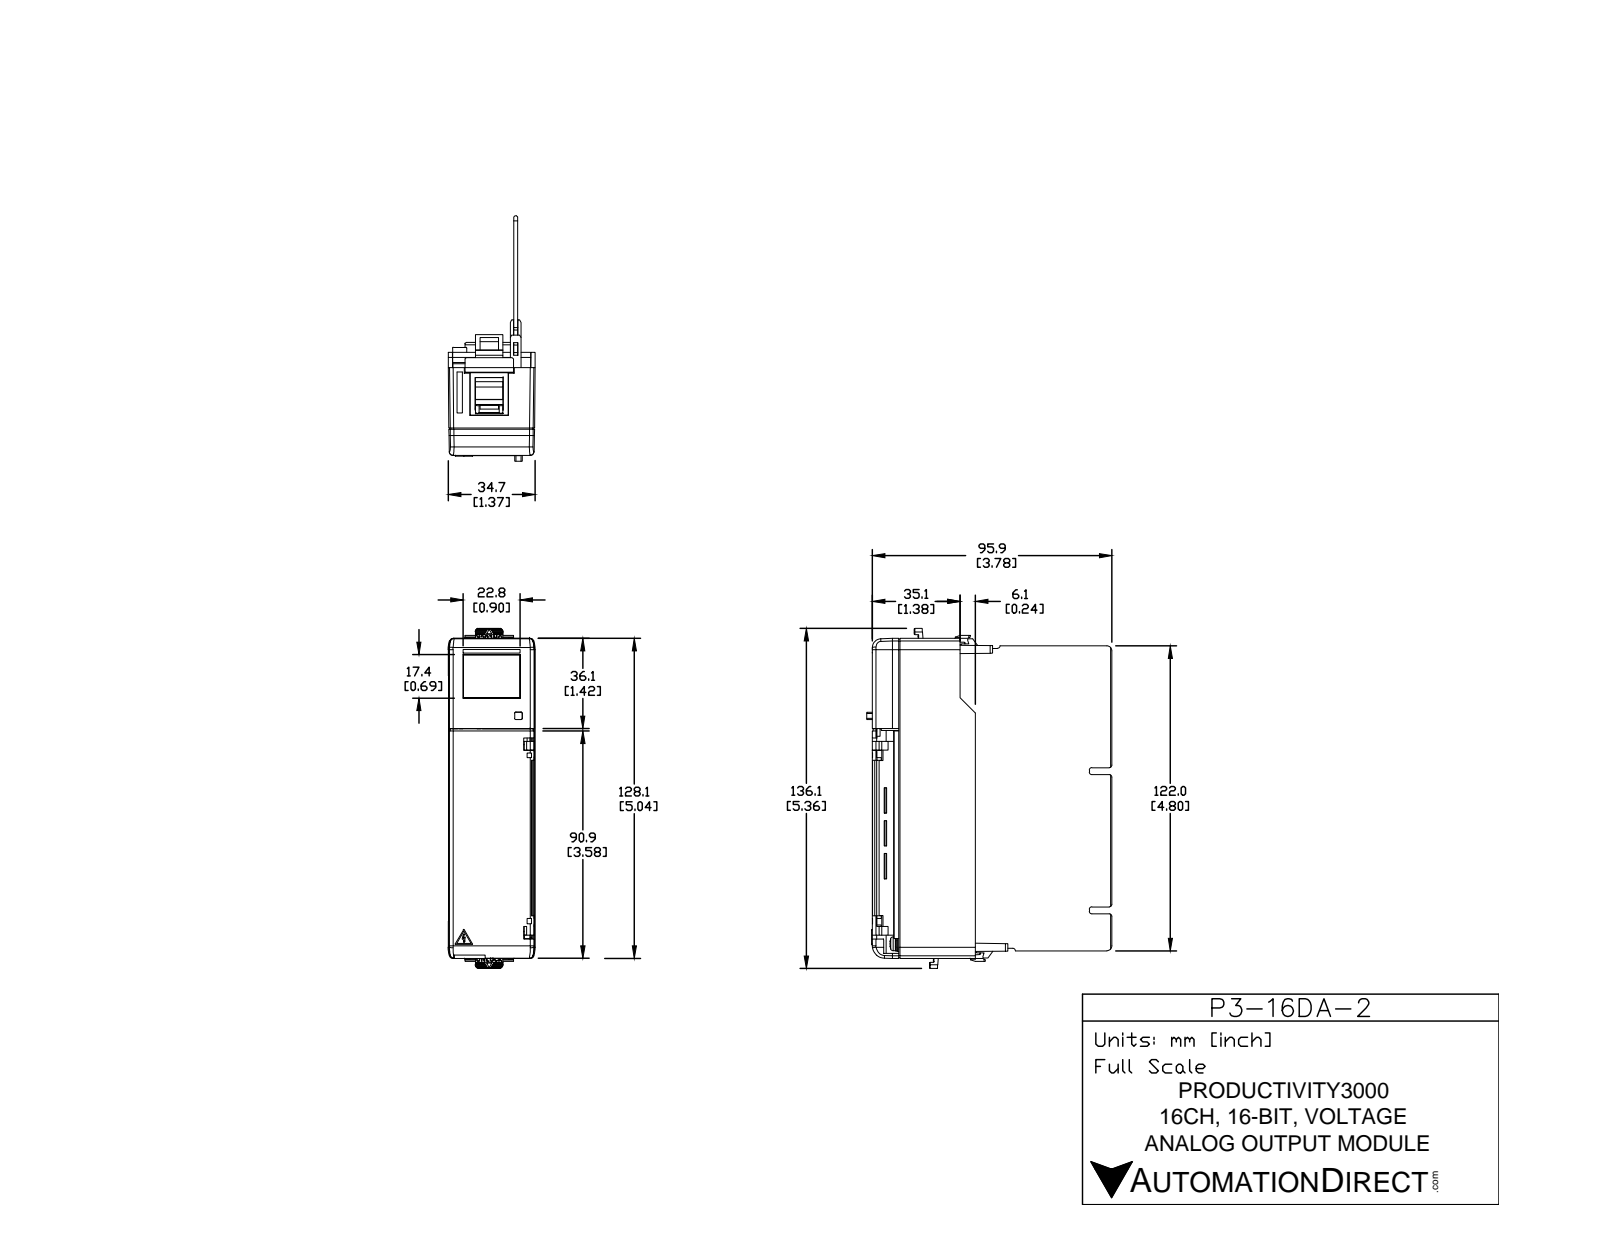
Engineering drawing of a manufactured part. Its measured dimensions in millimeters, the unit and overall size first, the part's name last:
Units: millimetres
Overall size (bounding box): 136.08 × 98.18 × 34.8
Round holes (diameter × count): ⌀3.2 ×22, ⌀5 ×2, ⌀1.8 ×1
Round bosses / shafts (diameter × count): ⌀5.5 ×22, ⌀3 ×22, ⌀2.4 ×20, ⌀5.6 ×2, ⌀2.2 ×2, ⌀2 ×2, ⌀1.5 ×1
Partial cylindrical surfaces — rounded edges, fillets, slot ends (radius × count): R0.5 ×95, R1 ×33, R0.3 ×29, R1.67 ×22, R1.5 ×13, R2 ×6, R0.2 ×5, R0.1 ×4
Main face-to-face distances: 1.6, 1.7, 28.23, 26.53, 32.56, 22.2, 2.2, 7.9, 6.8, 5.32
Hole centre spacings: 8.68, 7.62, 13.84, 15.24, 20.59, 22.86, 27.79, 30.48
Volume: 101 360 mm³ · Surface area: 75 361 mm²
Bodies: 1 solid, 3823 faces (2833 planar, 744 cylindrical, 246 other)
Part name (STEP PRODUCT): P3-16DA-2
STEP written by: SolidWorks 2009 (CONFIG_CONTROL_DESIGN)
